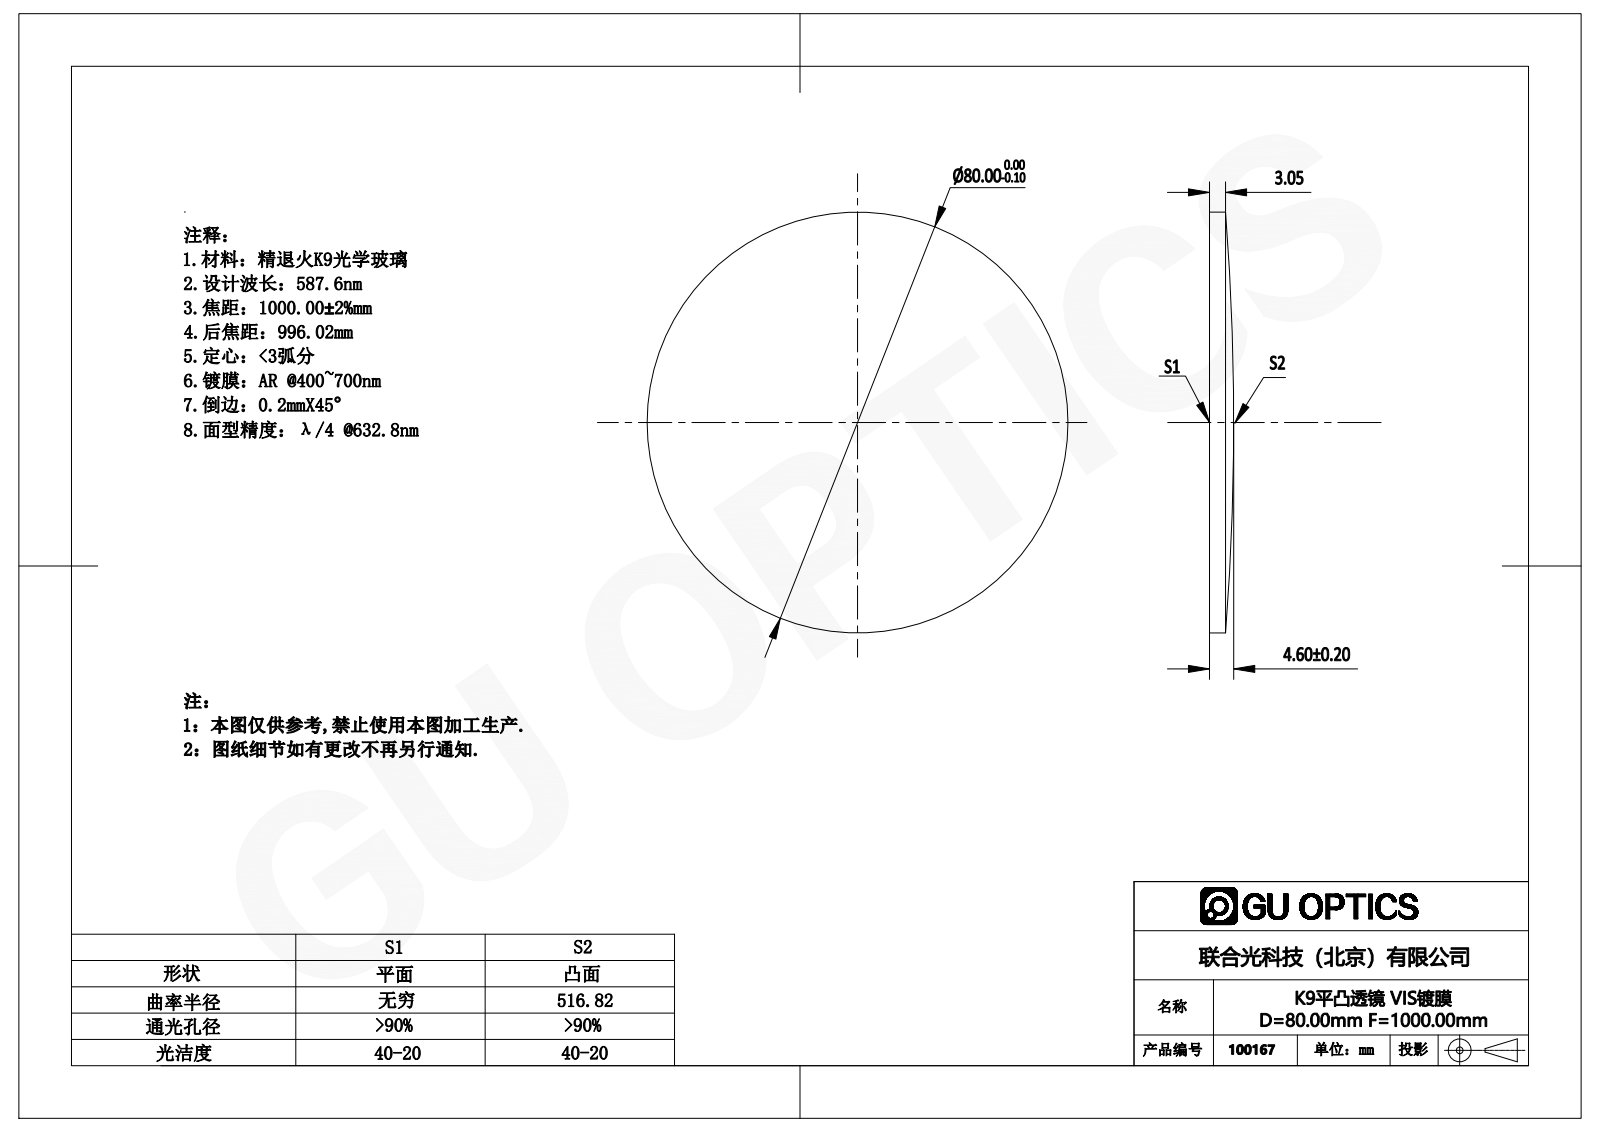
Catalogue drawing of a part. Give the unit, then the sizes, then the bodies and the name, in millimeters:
Units: millimetres
Overall size (bounding box): 80 × 80 × 6.12
Round bosses / shafts (diameter × count): ⌀80 ×1
Volume: 22 937 mm³ · Surface area: 10 838 mm²
Bodies: 1 solid, 5 faces (1 planar, 2 cylindrical, 2 other)
Part name (STEP PRODUCT): 100167
STEP written by: SolidWorks 2016 (AUTOMOTIVE_DESIGN)
